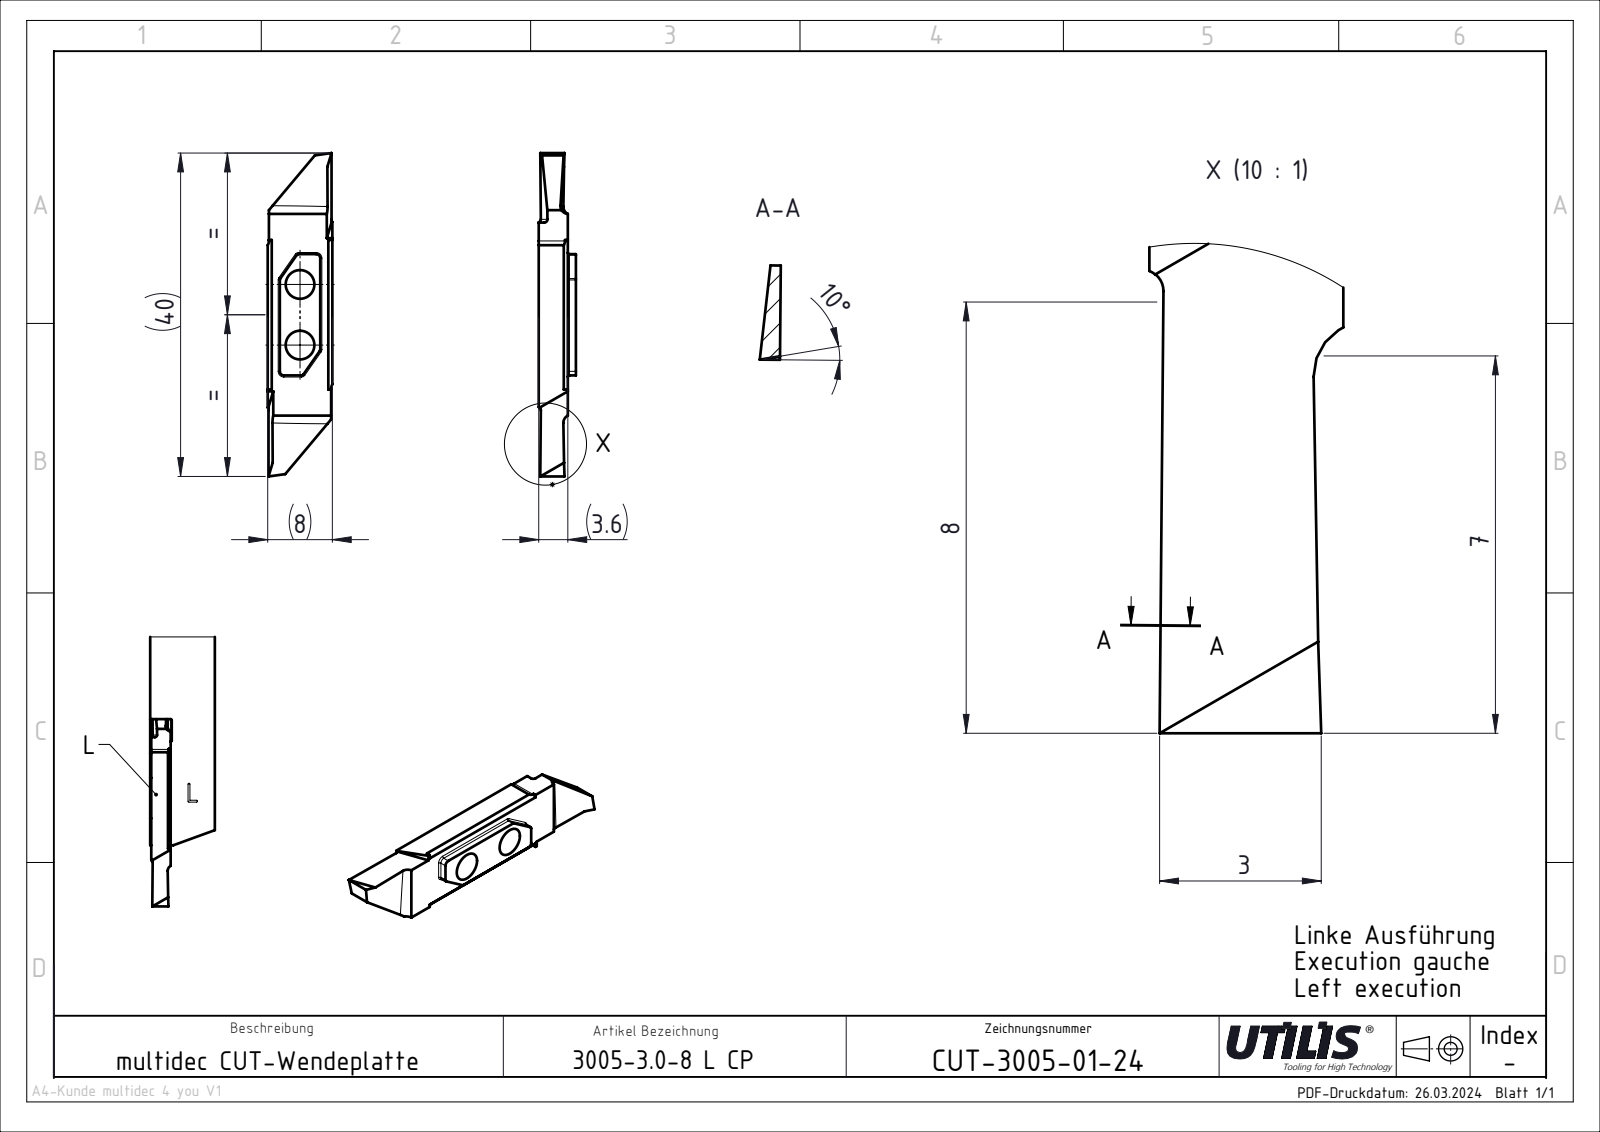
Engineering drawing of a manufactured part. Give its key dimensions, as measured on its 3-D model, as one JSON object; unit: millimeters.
{"part_name": "CUT-3005 CP; ASME Y14.5", "step_written_by": "SolidWorks 2023 SP4 || FormatWorks Professional (AP242_MANAGED_MODEL_BASED_3D_ENGINEERING_MIM_LF)", "units": "millimeters", "bodies": {"solids": 1, "faces": 30, "planar": 20, "cylindrical": 10, "other": 0}, "overall_size": [40, 8, 3.6], "volume_mm3": 857, "surface_area_mm2": 875, "round_holes": [[3.55, 2]], "partial_cylinders_radius": [[1, 4], [0.4, 2]], "face_to_face_distances": [3.6, 8, 22.54, 7.85, 7.7, 40, 10.75, 29.25, 18.5], "hole_center_spacings": [7.49]}
